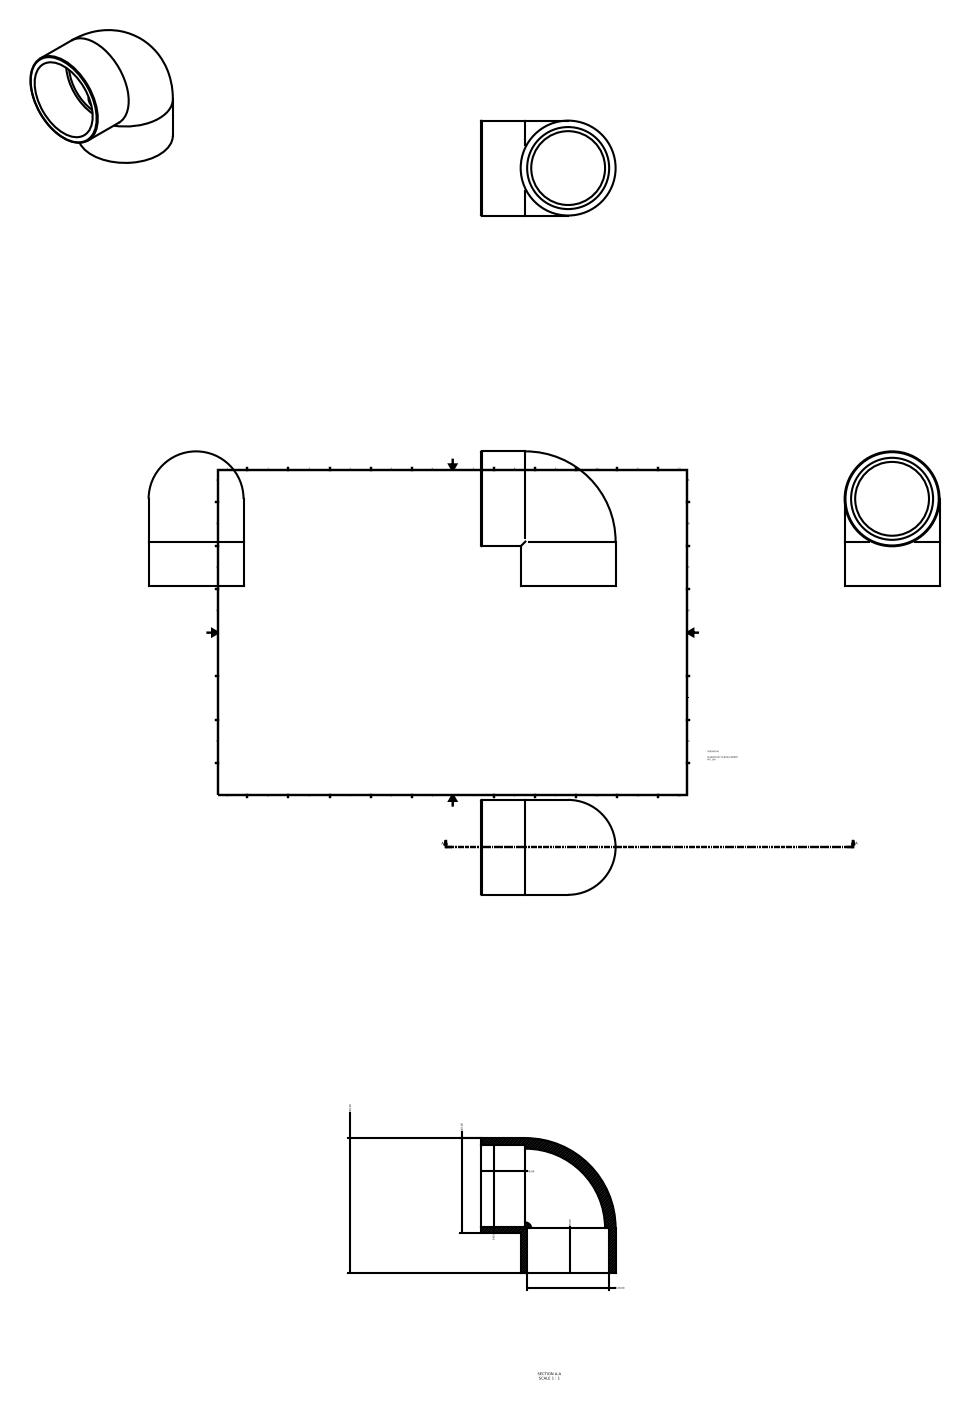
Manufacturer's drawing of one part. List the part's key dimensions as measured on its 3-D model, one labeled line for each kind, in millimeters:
Part name (STEP PRODUCT): 050500140
STEP written by: Autodesk Inventor 2015 (AUTOMOTIVE_DESIGN)
Units: millimetres
Bodies: 1 solid, 11 faces (4 planar, 4 cylindrical, 3 other)
Overall size (bounding box): 230 × 230 × 162
Volume: 1 752 000 mm³ · Surface area: 263 886 mm²
Round holes (diameter × count): ⌀140 ×2
Round bosses / shafts (diameter × count): ⌀162 ×2
Main face-to-face distances: 76
